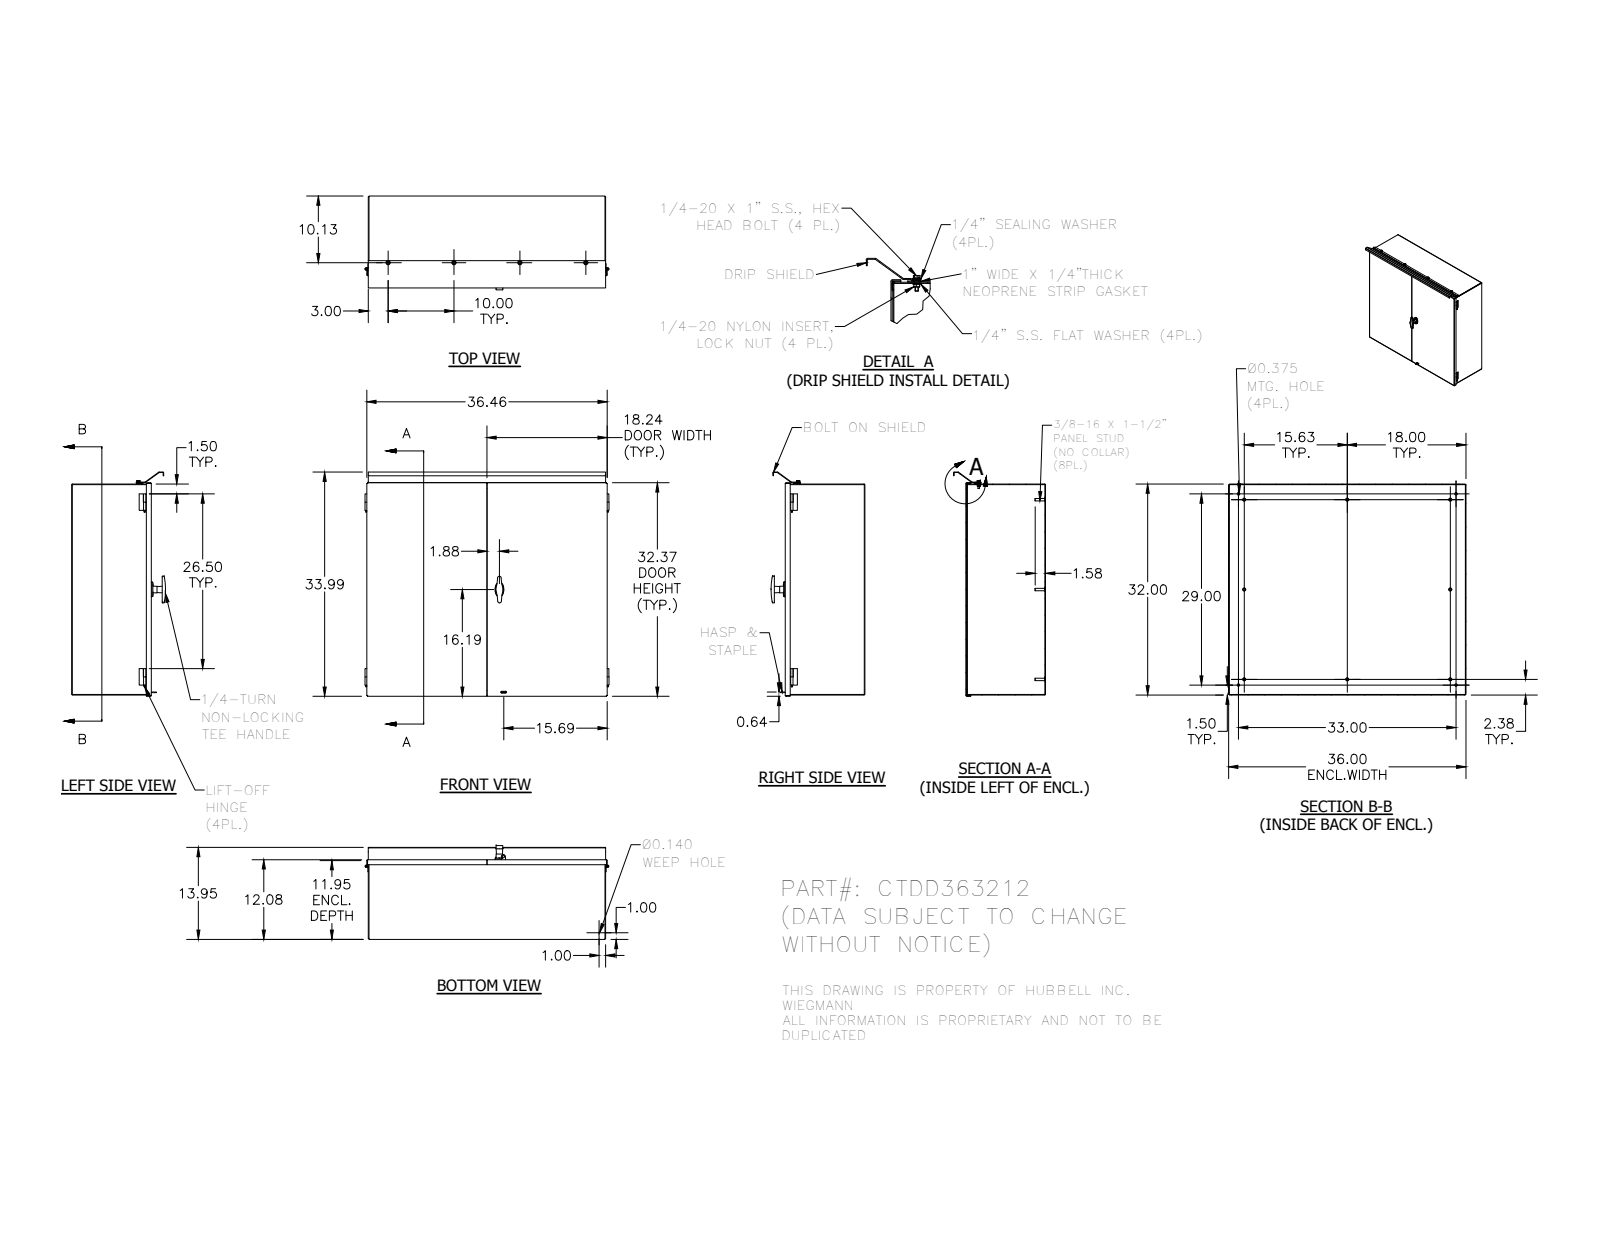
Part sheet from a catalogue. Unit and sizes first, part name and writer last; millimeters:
Units: millimetres
Overall size (bounding box): 939.8 × 863.47 × 361.56
Round holes (diameter × count): ⌀4.98 ×6, ⌀7.14 ×6, ⌀9.52 ×5, ⌀5.97 ×4, ⌀6.99 ×4, ⌀7.37 ×4, ⌀4.06 ×2, ⌀5.36 ×2, ⌀5.56 ×2, ⌀6.35 ×2, ⌀7.14 ×2, ⌀2.38 ×1
Round bosses / shafts (diameter × count): ⌀11.73 ×8, ⌀9.52 ×8, ⌀11.13 ×6, ⌀6.35 ×6, ⌀16.51 ×4, ⌀15.88 ×4, ⌀15.24 ×4, ⌀6.6 ×4
Partial cylindrical surfaces — rounded edges, fillets, slot ends (radius × count): R0.79 ×23, R3.17 ×13, R1.59 ×6, R2.67 ×6, R3.17 ×6, R0.2 ×2, R1.59 ×2, R3.97 ×2
Main face-to-face distances: 2.38, 304.4, 302.02, 306.78, 810.42, 812.8, 808.04, 2.37, 909.65, 912.03
Hole centre spacings: 254, 19.05, 508, 509.66, 522.9, 536.48, 583.17, 594.77
Volume: 7 080 000 mm³ · Surface area: 5 995 000 mm²
Bodies: 61 solids, 1024 faces (590 planar, 212 cylindrical, 222 other)
Part name (STEP PRODUCT): CTDD363212BTB; CTDD3212LRS; 38822; HC2527 (+8 more)
STEP written by: Autodesk Inventor 2014 (AUTOMOTIVE_DESIGN)
